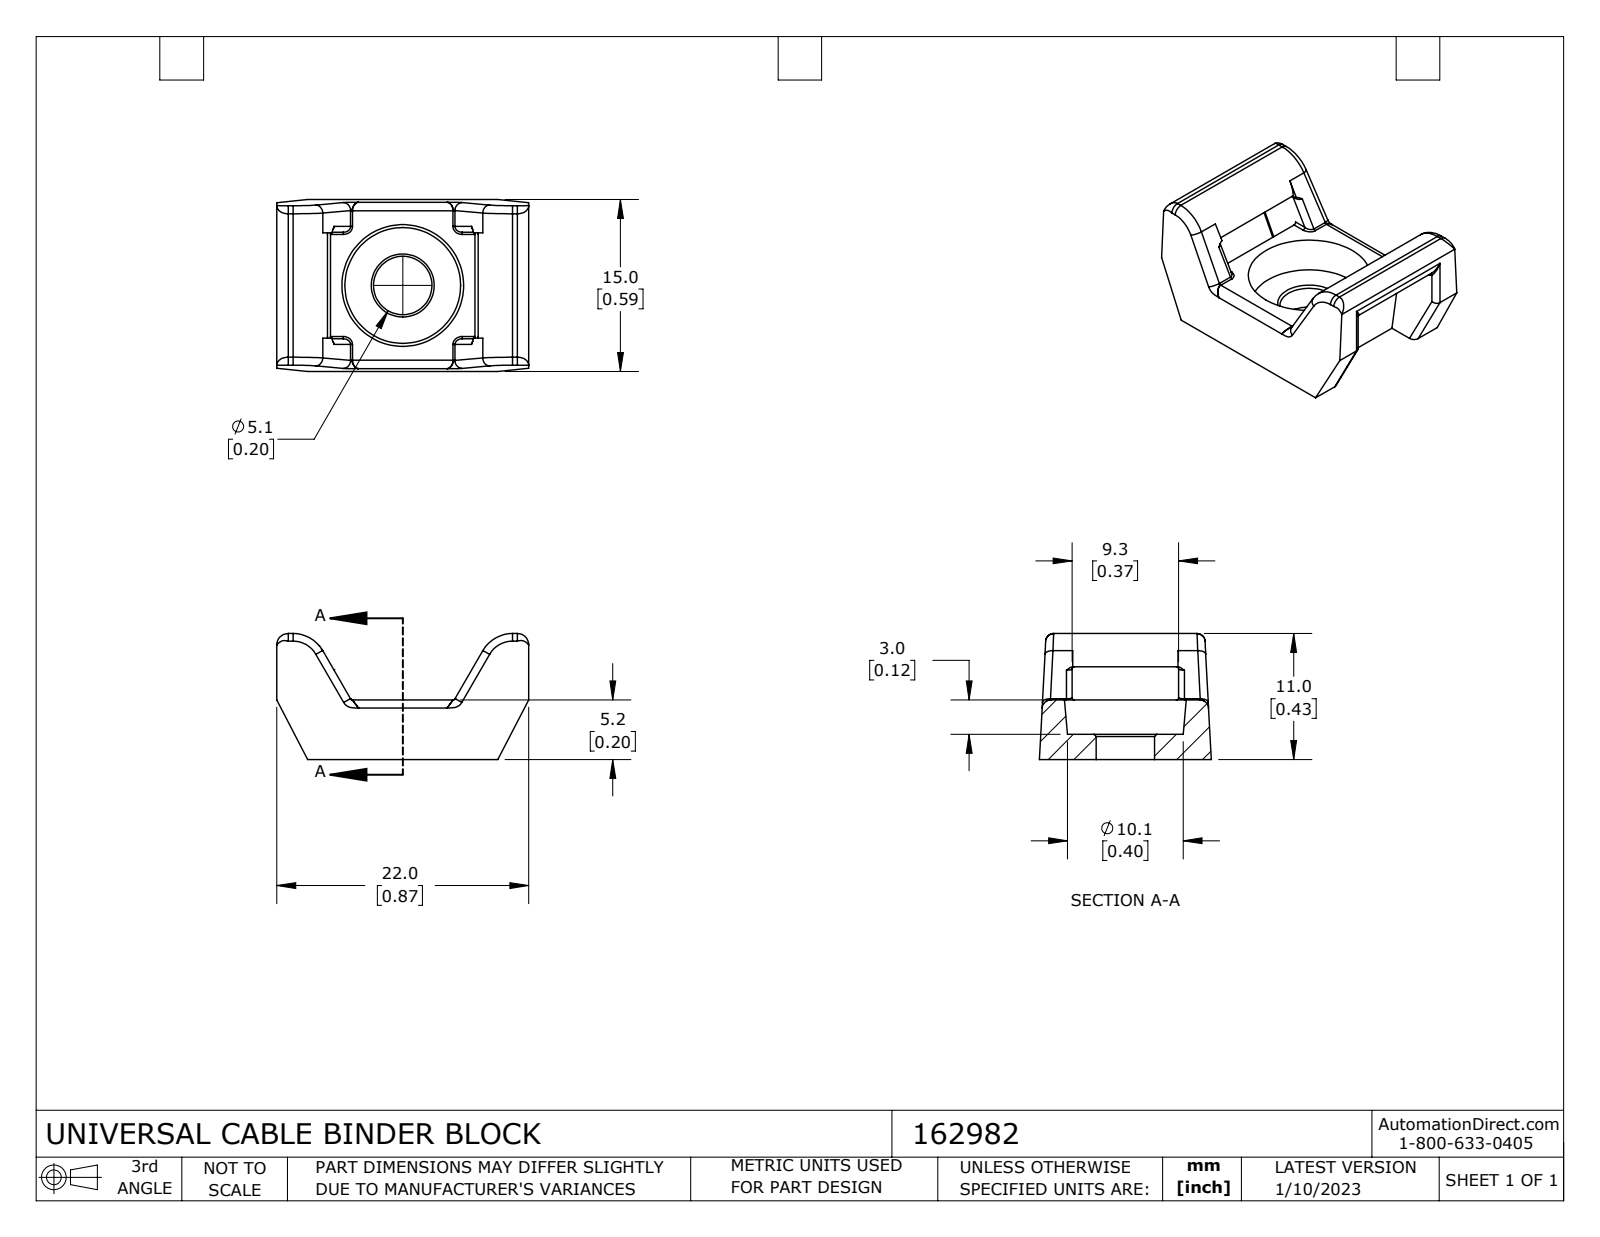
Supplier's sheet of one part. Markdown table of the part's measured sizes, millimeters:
| quantity | value |
| --- | --- |
| part name | 162982 |
| STEP written by | SolidWorks 2021 (CONFIG_CONTROL_DESIGN) |
| units | millimeters |
| bodies | 1 solid, 107 faces (29 planar, 42 cylindrical, 36 other) |
| overall size | 22 × 15 × 11 |
| volume | 1 300 mm³ |
| surface area | 1 405 mm² |
| round holes (diameter × count) | 5.1 × 1 |
| partial cylindrical surfaces (radius × count) | 0.5 × 12, 0.2 × 6, 0.7 × 6, 0.8 × 2, 1 × 2, 1.3 × 2, 3 × 2 |
| main face-to-face distances | 2.9, 5.2, 9.3, 2.2, 3, 8.1, 5.9, 22, 11, 8.8 |
